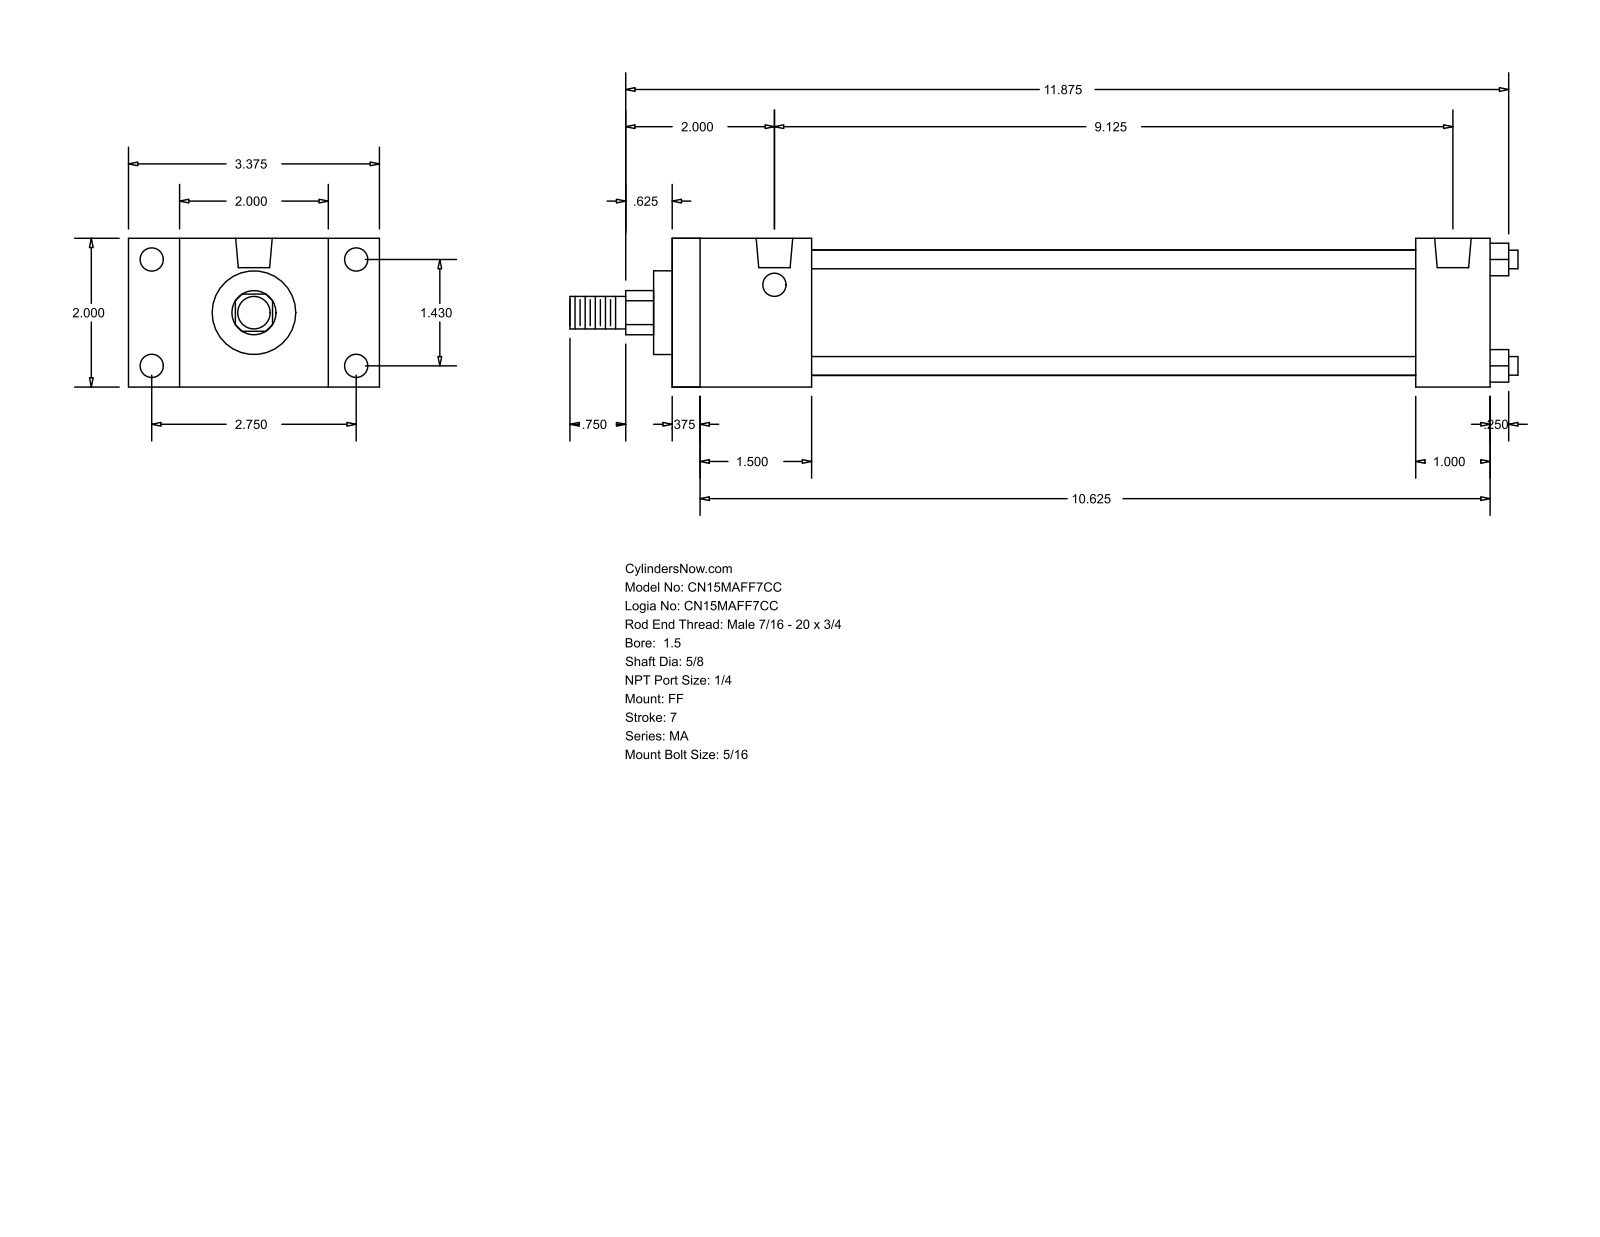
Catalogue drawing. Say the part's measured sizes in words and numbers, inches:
The part is named "MA_FF__0150_0.625". Its 3-D file was written by "GSSL Pune (CONFIG_CONTROL_DESIGN)". It is 0 solids with 92 faces: 64 planar, 28 cylindrical and 0 other. Overall it measures 12.75 by 3.375 by 2 inches. Round holes: 8 of diameter 0.313, 2 of diameter 0.492. Round bosses or shafts: 4 of diameter 0.25, 1 of diameter 1.69, 1 of diameter 1.125, 1 of diameter 0.625, 1 of diameter 0.437. Partial cylindrical surfaces (rounded edges, fillets, slot ends): 1 of radius 0.297. The main face-to-face distances are 2, 11, 0.375, 10.625, 1.875, 10, 1.5, 9.625, 8.125, 9.125. The hole center spacings are 1.43, 2.75, 3.099, 9.125.
